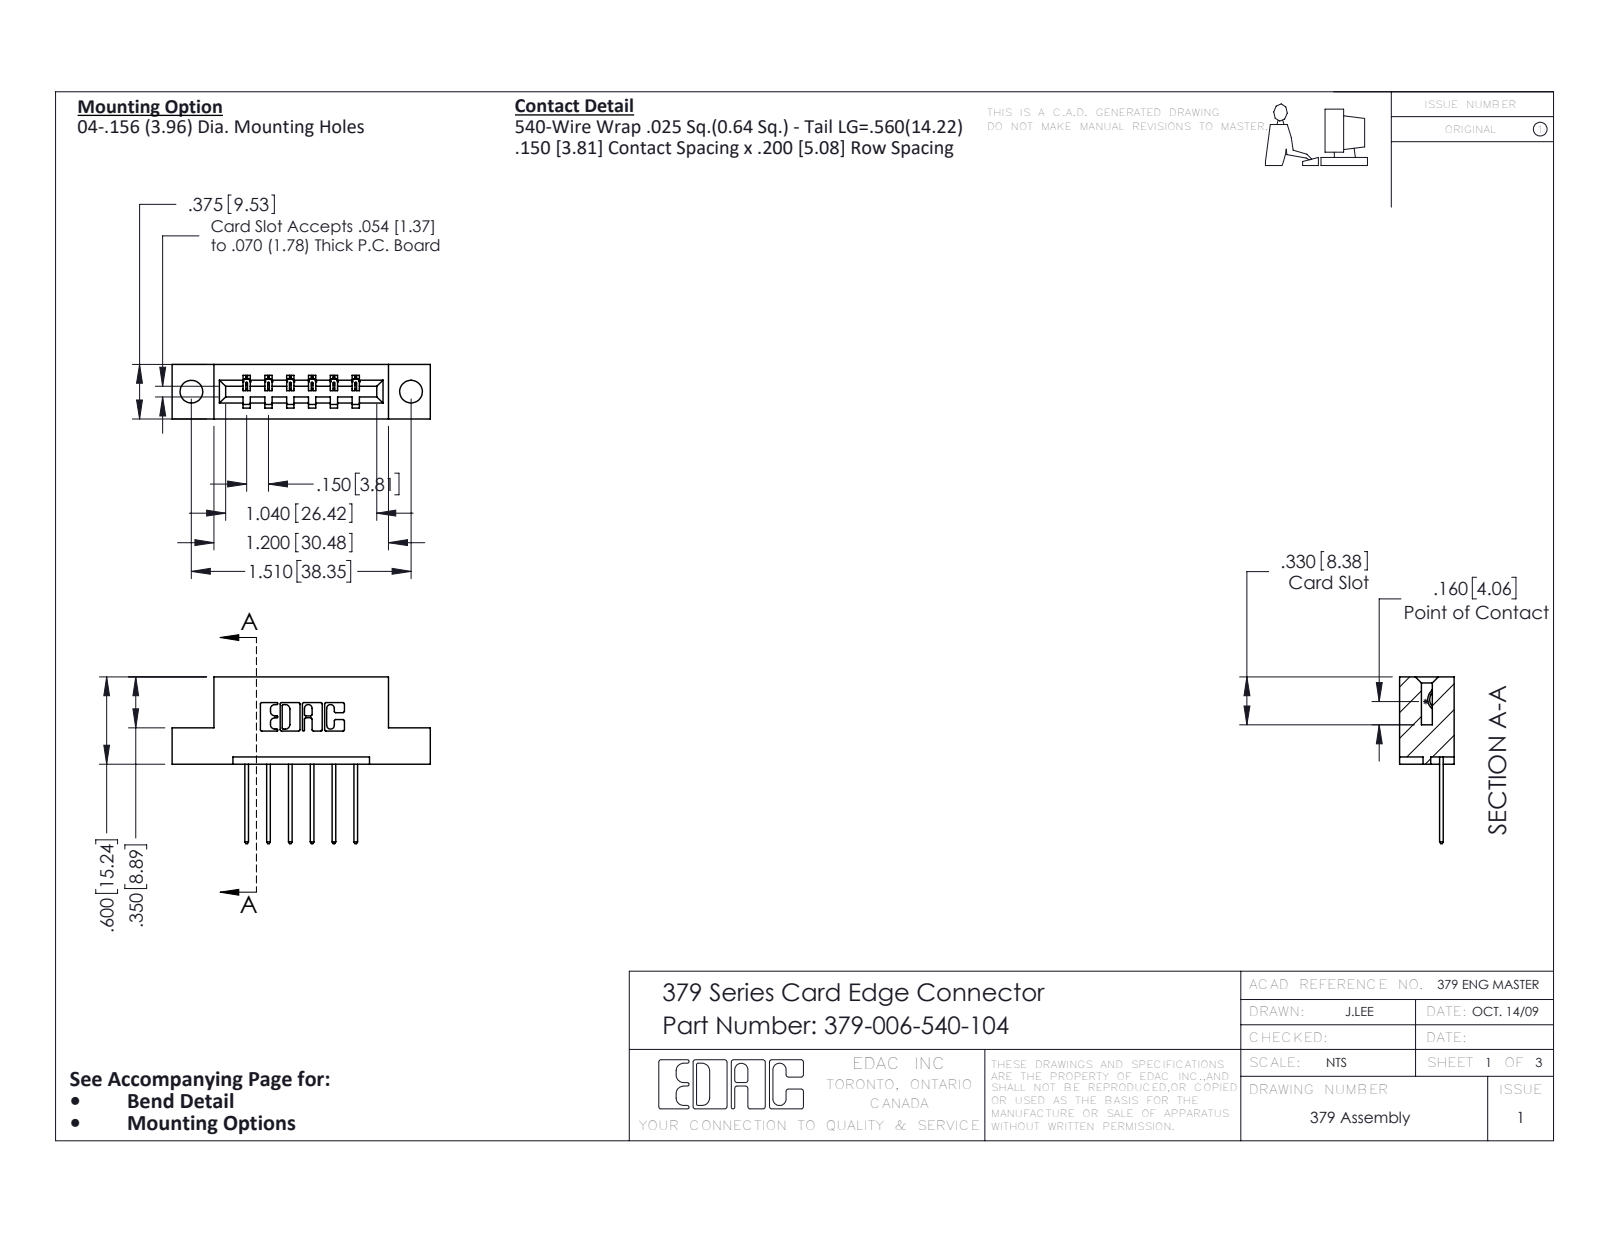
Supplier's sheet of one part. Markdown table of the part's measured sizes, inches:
| quantity | value |
| --- | --- |
| part name | 379 Part_Flush - .156 Dia - TH; 379-006-540-104; 345-292-001_345-293-140 |
| STEP written by | SolidWorks 2016 (CONFIG_CONTROL_DESIGN) |
| units | inches |
| bodies | 7 solids, 462 faces (322 planar, 140 cylindrical, 0 other) |
| overall size | 1.775 × 1.147 × 0.375 |
| volume | 0.258 in³ |
| surface area | 6.203 in² |
| round holes (diameter × count) | 0.156 × 2 |
| partial cylindrical surfaces (radius × count) | 0.01 × 22, 0.006 × 12, 0.01 × 12, 0.007 × 6, 0.031 × 6, 0.026 × 3, 0.014 × 1, 0.022 × 1 |
| main face-to-face distances | 0.3, 0.2, 0.375, 0.05, 0.15, 0.075, 0.1, 0.25, 0.35, 0.6 |
| hole center spacings | 1.51 |
